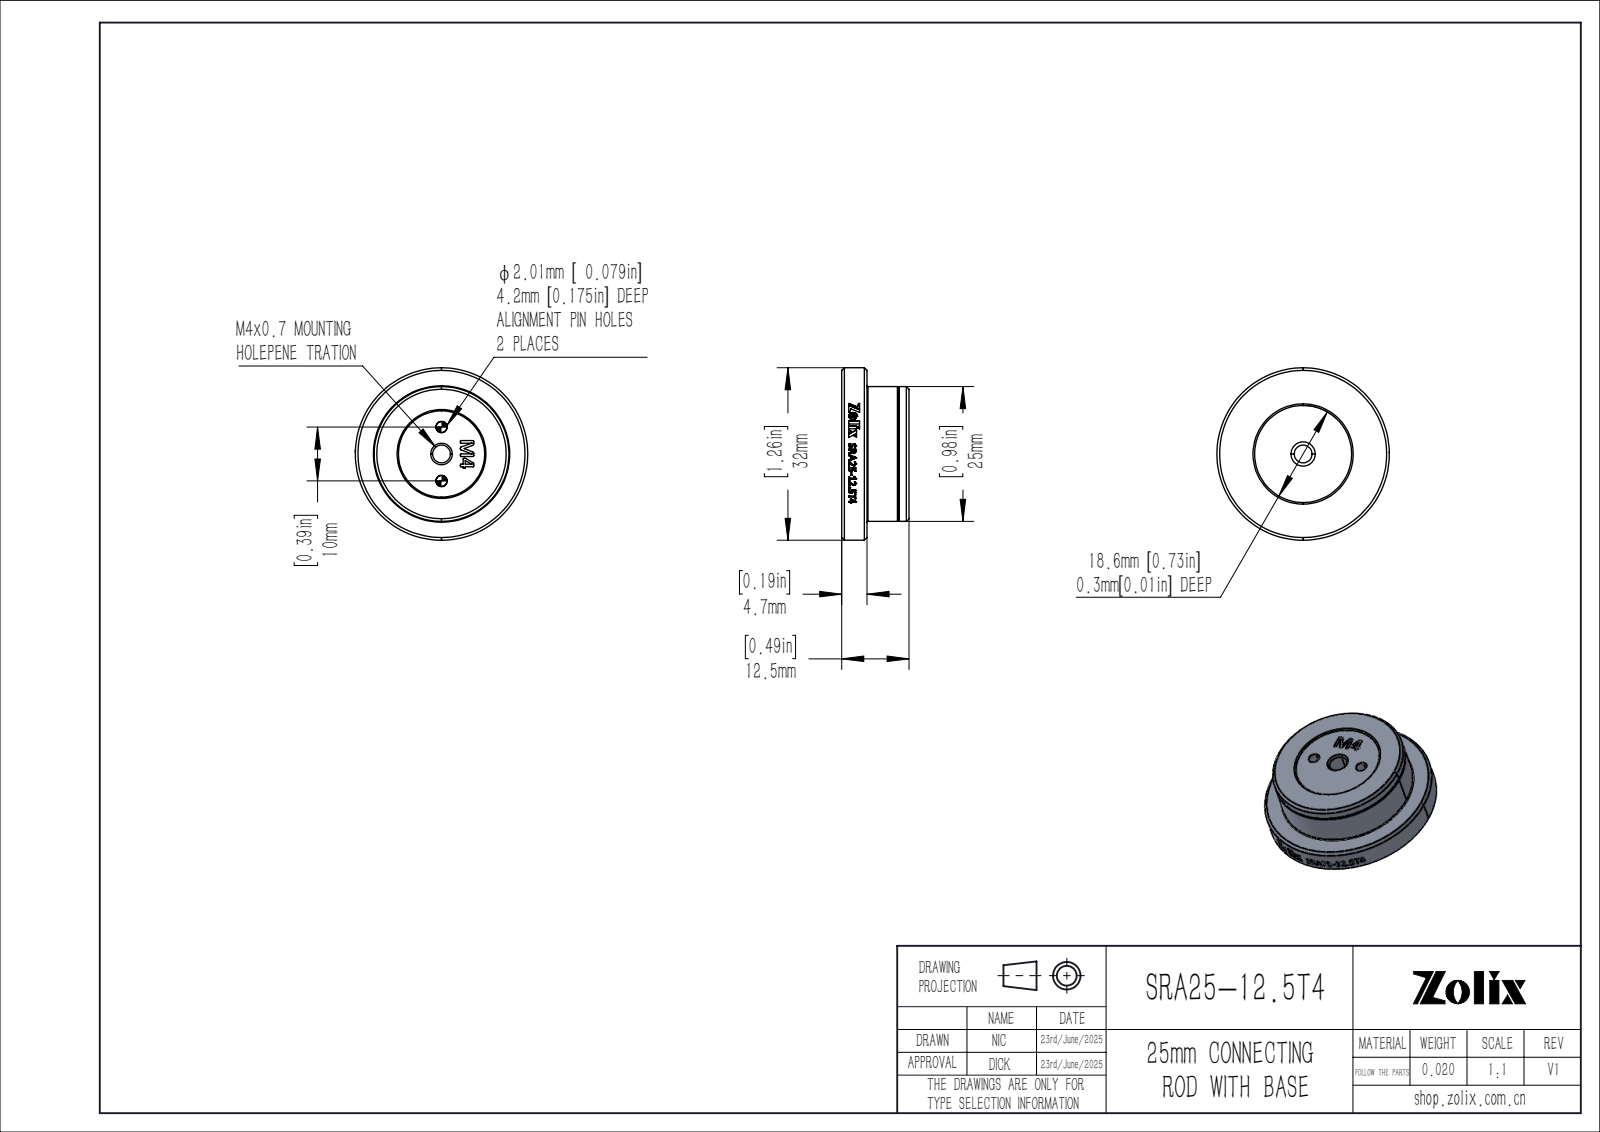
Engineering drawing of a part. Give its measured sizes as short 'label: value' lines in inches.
name: SRA25-12.5T4
written by: SolidWorks 2020 (CONFIG_CONTROL_DESIGN)
unit: in
bodies: 1 solid, 446 faces (95 planar, 37 cylindrical, 314 other)
size: 1.26 × 1.26 × 0.492
volume: 0.446 in³; area: 4.34 in²
holes: 2× ⌀0.079, 1× ⌀0.13
bosses: 1× ⌀1.26, 1× ⌀0.984
rounds: 1× R0.629
face distances: 0.185, 0.48, 0.173, 0.492, 0.307, 0.482, 0.47, 0.297, 0.469, 0.295
hole spacings: 0.197, 0.394
